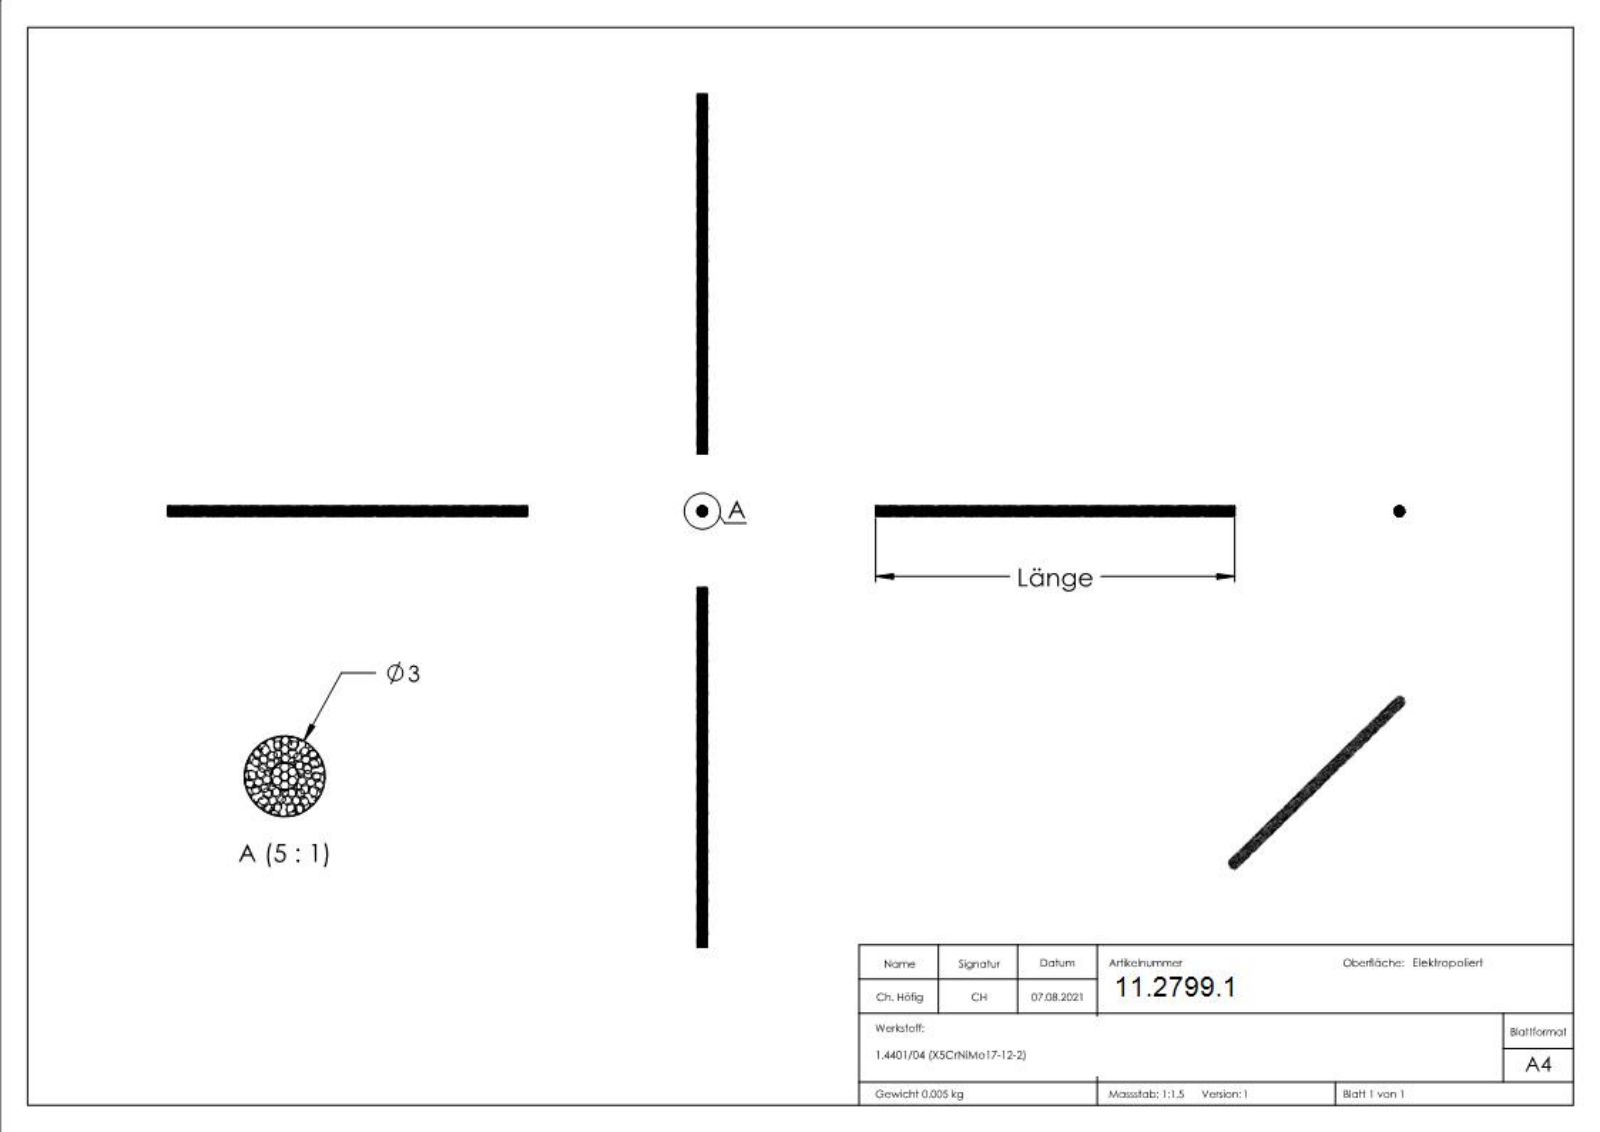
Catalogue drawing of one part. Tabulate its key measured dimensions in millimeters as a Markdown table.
| quantity | value |
| --- | --- |
| part name | 101000003 |
| STEP written by | SolidWorks 2018 (CONFIG_CONTROL_DESIGN) |
| units | millimeters |
| bodies | 58 solids, 223 faces (116 planar, 3 cylindrical, 104 other) |
| overall size | 101 × 6 × 6 |
| volume | 612 mm³ |
| surface area | 6 326 mm² |
| round bosses / shafts (diameter × count) | 6 × 1, 1.1 × 1, 0.33 × 1 |
| main face-to-face distances | 1, 100, 101 |
